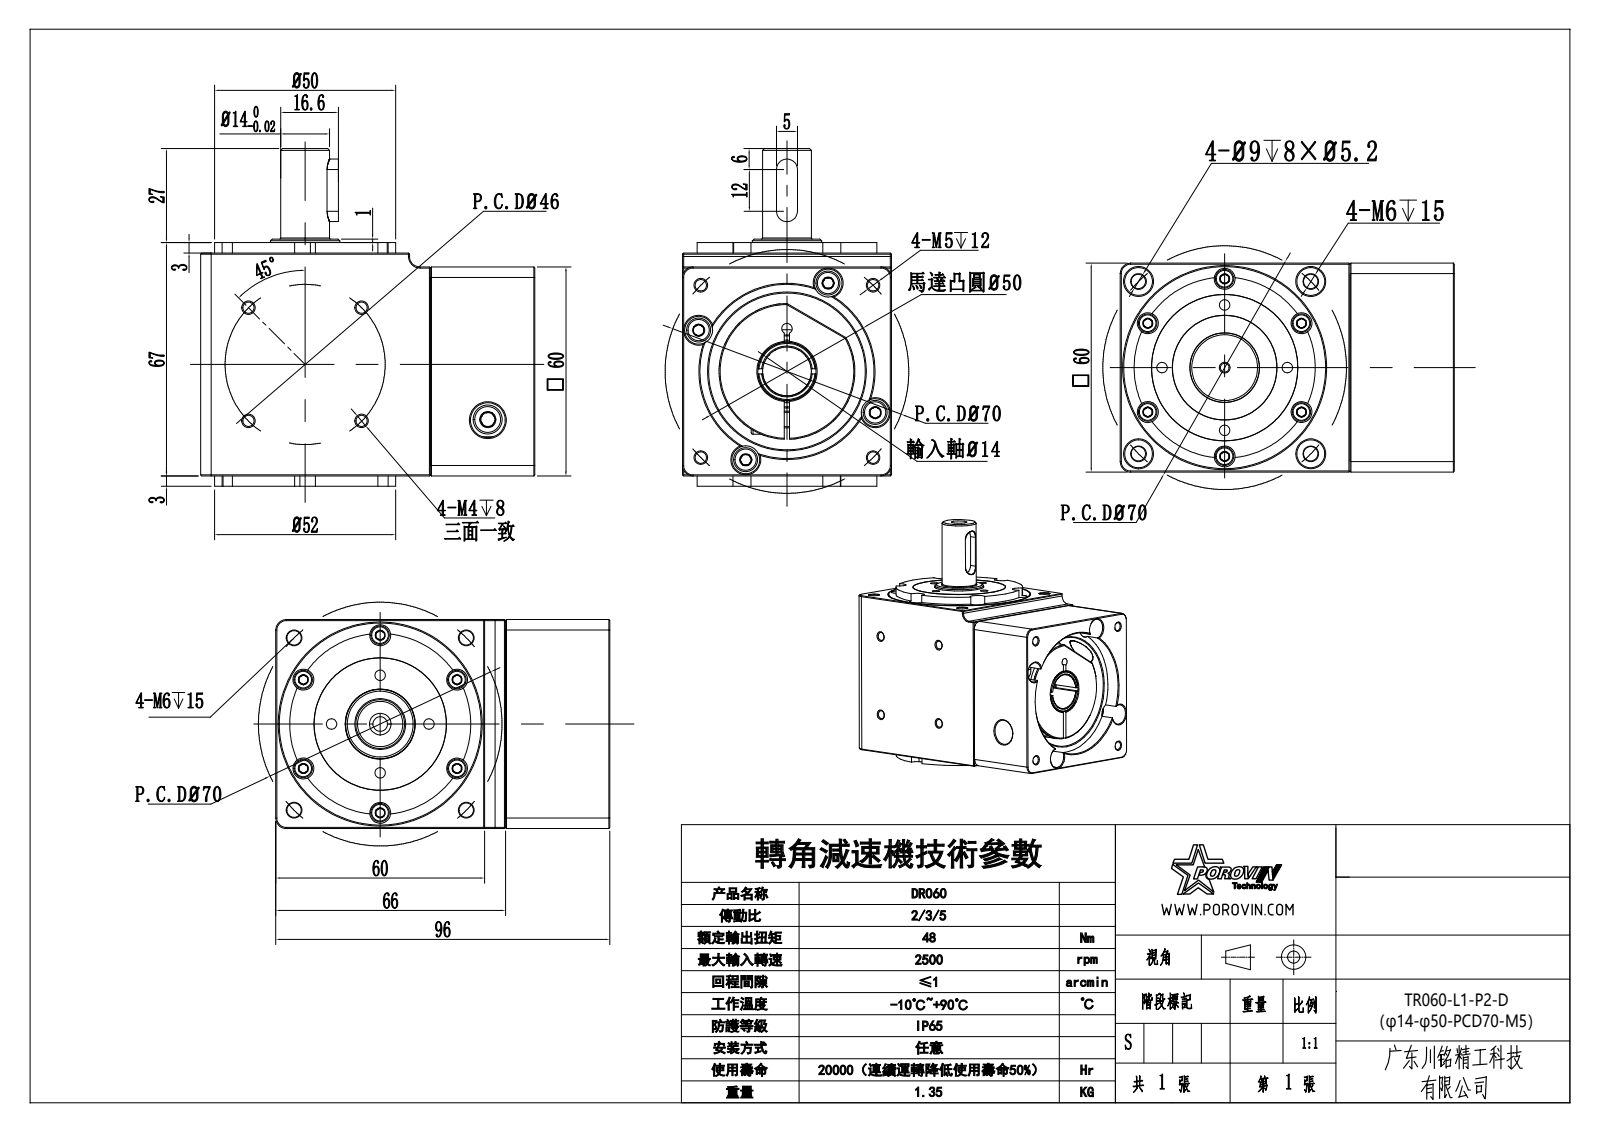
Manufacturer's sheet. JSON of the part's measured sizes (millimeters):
{"part_name": "DR060-02_03-05_-14-30-50-70-M5", "step_written_by": "CREO PARAMETRIC BY PTC INC, 2018070 (CONFIG_CONTROL_DESIGN)", "units": "millimeters", "bodies": {"solids": 1, "faces": 1025, "planar": 376, "cylindrical": 275, "other": 374}, "overall_size": [97.01, 96, 60], "volume_mm3": 330830, "surface_area_mm2": 58389, "round_holes": [[3.3, 12], [3, 9], [3.5, 6], [4.2, 6], [6, 6], [4.5, 4], [5.1, 4], [8, 4], [9, 4], [10, 2], [2.5, 1], [5.5, 1]], "round_bosses_or_shafts": [[5.5, 6], [2.87, 6], [7, 4], [3.84, 4], [58, 1], [39, 1], [30, 1], [19.9, 1]], "partial_cylinders_radius": [[3, 7], [2.5, 2], [5.5, 1], [25, 1], [26, 1], [27.45, 1]], "face_to_face_distances": [60, 3, 67, 4, 7, 63, 70, 64, 24, 96], "hole_center_spacings": [25.5, 22.8, 25.65, 26.98, 32.52, 35, 45.98, 49.4]}
